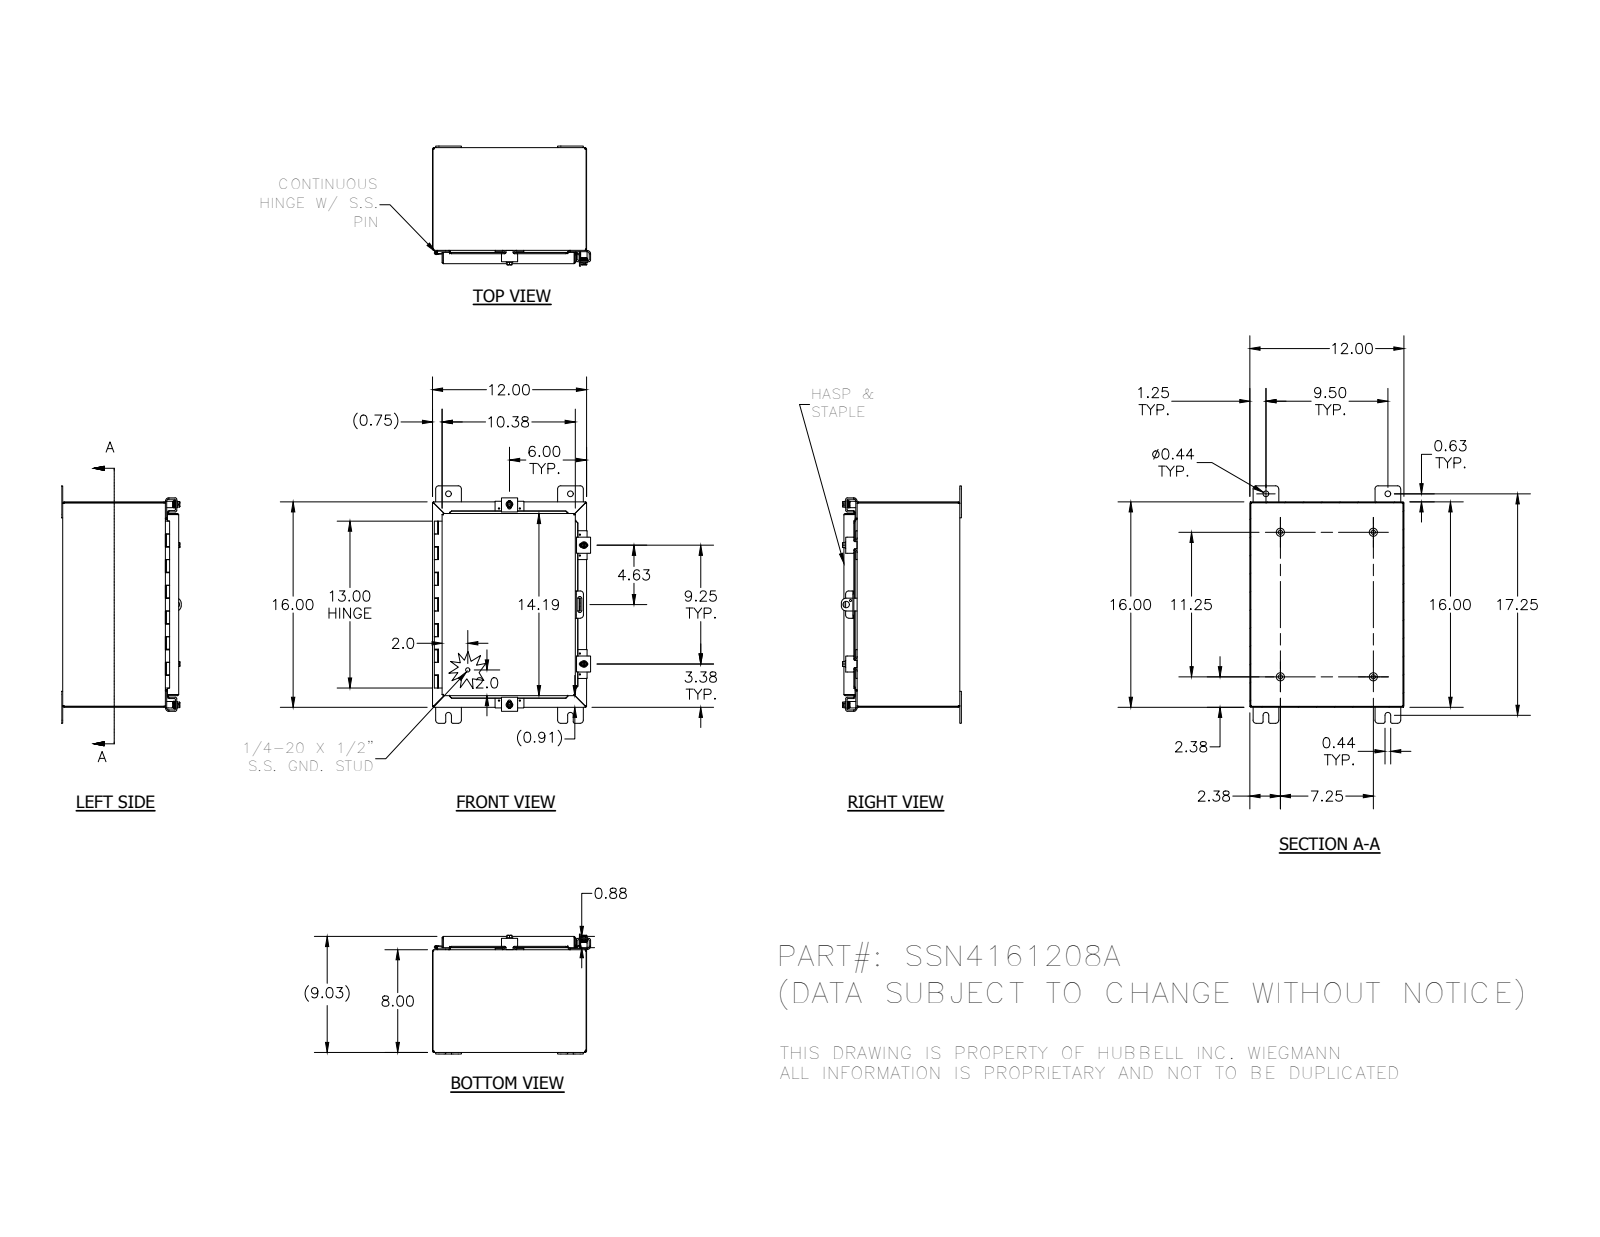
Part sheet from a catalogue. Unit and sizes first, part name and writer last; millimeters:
Units: millimetres
Overall size (bounding box): 469.9 × 310.3 × 237.6
Round holes (diameter × count): ⌀2.8 ×8, ⌀5.4 ×4, ⌀7.1 ×4, ⌀7.6 ×4, ⌀11.1 ×4, ⌀3.2 ×1, ⌀4 ×1, ⌀12.7 ×1
Round bosses / shafts (diameter × count): ⌀8.4 ×6, ⌀6.4 ×6, ⌀15.9 ×4, ⌀13.2 ×4, ⌀12.7 ×4, ⌀8.9 ×4, ⌀8.6 ×1, ⌀3 ×1
Partial cylindrical surfaces — rounded edges, fillets, slot ends (radius × count): R0.8 ×49, R3.2 ×33, R6.4 ×29, R0.8 ×23, R2.7 ×23, R1.6 ×14, R1.8 ×8, R3.6 ×8
Main face-to-face distances: 1.9, 227.6, 302.9, 404.5, 225.7, 229.4, 201.3, 26.2, 304.8, 301
Hole centre spacings: 22.3, 388.9, 235, 22.3, 41.3, 41.3, 100.1, 104.1
Volume: 1 328 000 mm³ · Surface area: 1 361 000 mm²
Bodies: 37 solids, 1384 faces (551 planar, 592 cylindrical, 241 other)
Part name (STEP PRODUCT): 14x10; 38412; SSN4161208ABKP; 32874-16P (+8 more)
STEP written by: SolidWorks 2014 (AUTOMOTIVE_DESIGN)
